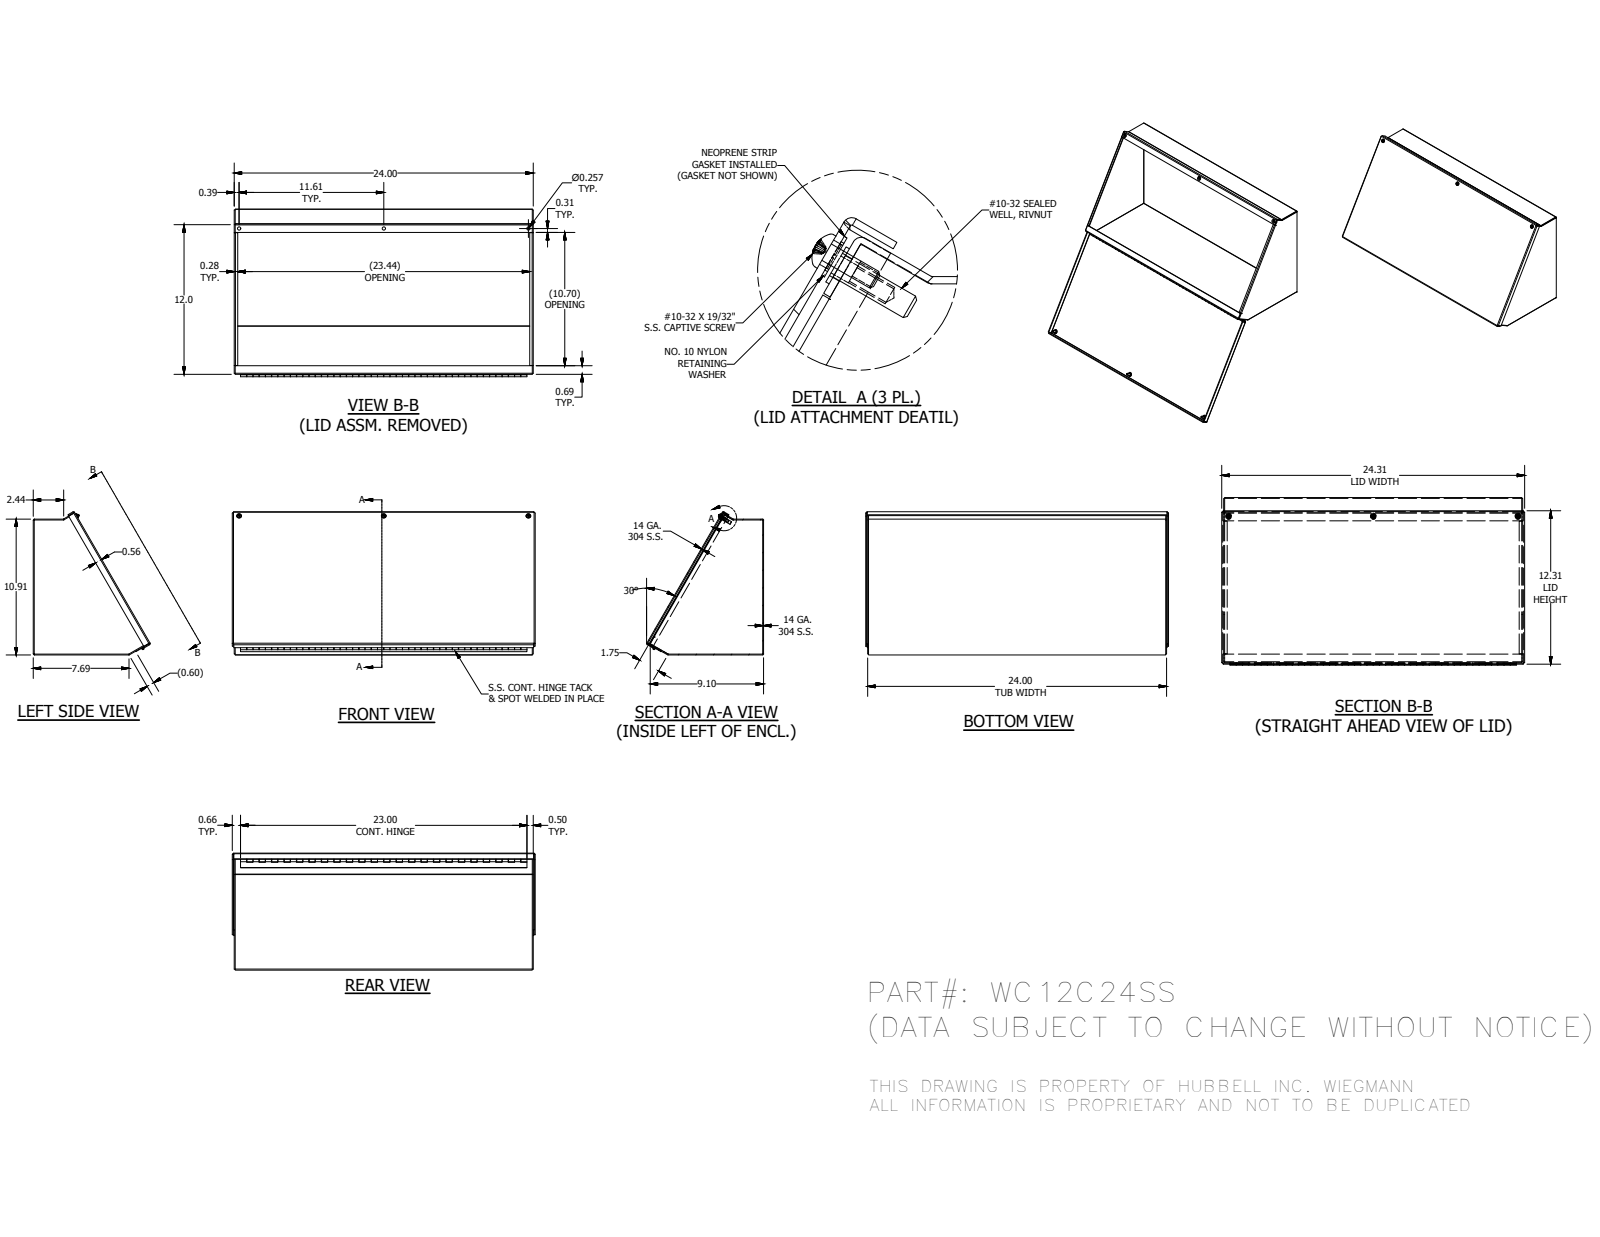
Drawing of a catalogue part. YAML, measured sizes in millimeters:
part_name: "WC12C24SSBTB; WC12C24SSLID; WC12CSSLS; WC12CSSRS (+8 more)"
step_written_by: "Autodesk Inventor 2014 (AUTOMOTIVE_DESIGN)"
units: millimeters
bodies: {solids: 16, faces: 597, planar: 364, cylindrical: 159, other: 74}
overall_size: [617.54, 292.01, 238.43]
volume: 1317000
surface_area: 1439000
round_holes:
  - {diameter: 3.96, count: 3}
  - {diameter: 4.98, count: 3}
  - {diameter: 6.53, count: 3}
  - {diameter: 7.06, count: 3}
  - {diameter: 7.14, count: 3}
  - {diameter: 2.96, count: 1}
round_bosses_or_shafts:
  - {diameter: 11.51, count: 3}
  - {diameter: 10.31, count: 3}
  - {diameter: 9.47, count: 3}
  - {diameter: 6.3, count: 3}
  - {diameter: 4.83, count: 3}
  - {diameter: 5.08, count: 1}
  - {diameter: 2.54, count: 1}
partial_cylinders:
  - {radius: 0.4, count: 12}
  - {radius: 2.28, count: 12}
  - {radius: 2.27, count: 3}
face_to_face_distances: [1.88, 607.72, 275.14, 605.84, 609.6, 273.26, 277.02, 2.94, 304.8, 1.06]
hole_center_spacings: [294.97, 589.94, 1.51]
